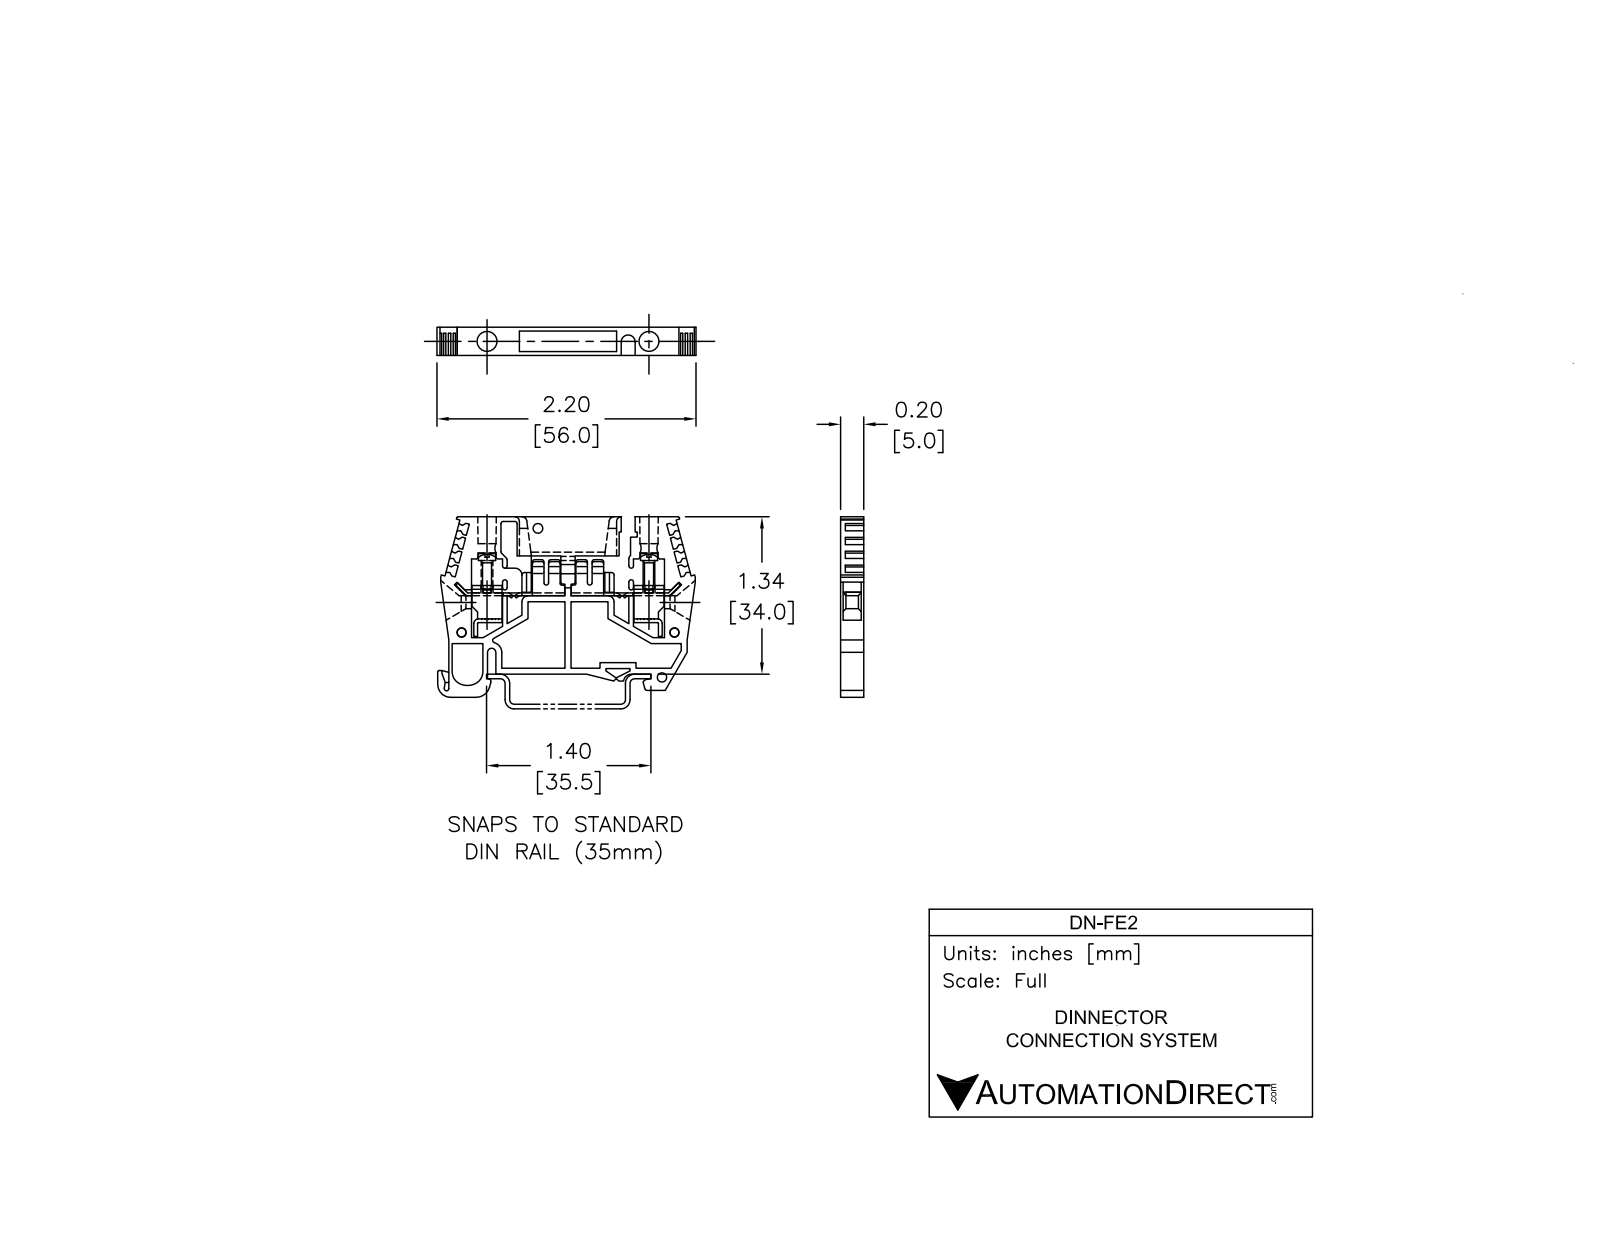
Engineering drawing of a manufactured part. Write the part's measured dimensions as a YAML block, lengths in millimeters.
part_name: "4358000_DN-QFE2"
step_written_by: "SolidWorks 2013 (AUTOMOTIVE_DESIGN)"
units: millimeters
bodies: {solids: 1, faces: 281, planar: 195, cylindrical: 62, other: 24}
overall_size: [55.65, 39, 5]
volume: 7480
surface_area: 5923
round_holes:
  - {diameter: 2, count: 3}
  - {diameter: 4.1, count: 2}
partial_cylinders:
  - {radius: 0.5, count: 11}
  - {radius: 3, count: 5}
  - {radius: 1, count: 3}
  - {radius: 0.9, count: 1}
  - {radius: 1.05, count: 1}
  - {radius: 1.5, count: 1}
  - {radius: 1.7, count: 1}
  - {radius: 1.95, count: 1}
face_to_face_distances: [5, 34, 2.2, 4.45, 0.55, 1, 3.1, 3.45, 3.6, 1.4]
hole_center_spacings: [10.07, 35, 44.38, 46]
